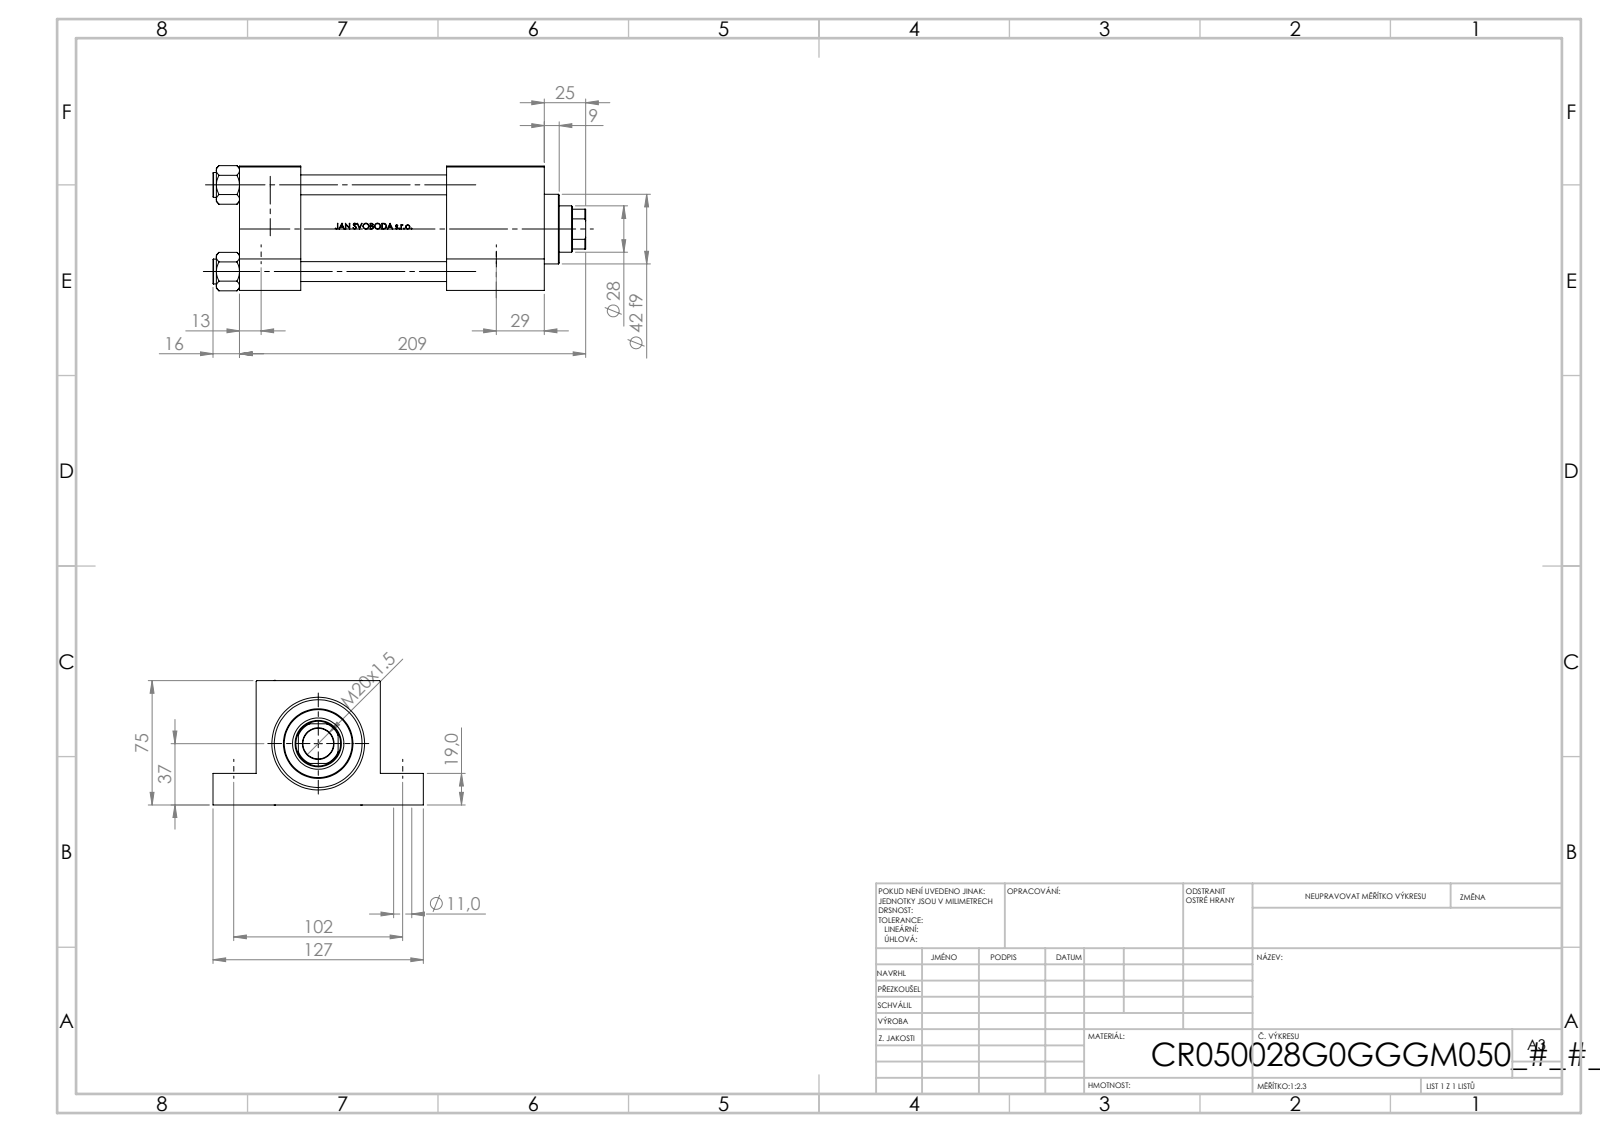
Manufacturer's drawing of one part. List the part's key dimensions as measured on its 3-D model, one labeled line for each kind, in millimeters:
Part name (STEP PRODUCT): V215CR_VCP_G; V215CR_G_Body; V215CR_G_TYCINKA; NUT_M5_G (+1 more)
STEP written by: SolidWorks 2019 (CONFIG_CONTROL_DESIGN)
Units: millimetres
Bodies: 11 solids, 1088 faces (432 planar, 124 cylindrical, 532 other)
Overall size (bounding box): 225 × 127 × 75.54
Volume: 814 905 mm³ · Surface area: 180 164 mm²
Round holes (diameter × count): ⌀11 ×4, ⌀12 ×4, ⌀7 ×2, ⌀20.96 ×2, ⌀30 ×2, ⌀18.5 ×1, ⌀28 ×1, ⌀31 ×1, ⌀41 ×1, ⌀50 ×1, ⌀53 ×1
Round bosses / shafts (diameter × count): ⌀15 ×4, ⌀56 ×1, ⌀42 ×1
Partial cylindrical surfaces — rounded edges, fillets, slot ends (radius × count): R13.5 ×1
Main face-to-face distances: 75, 37, 184, 147, 19, 56, 101, 125, 88, 59
Hole centre spacings: 52.3, 36.63, 37.34, 51.3, 52.63, 73.96, 102, 138.72
